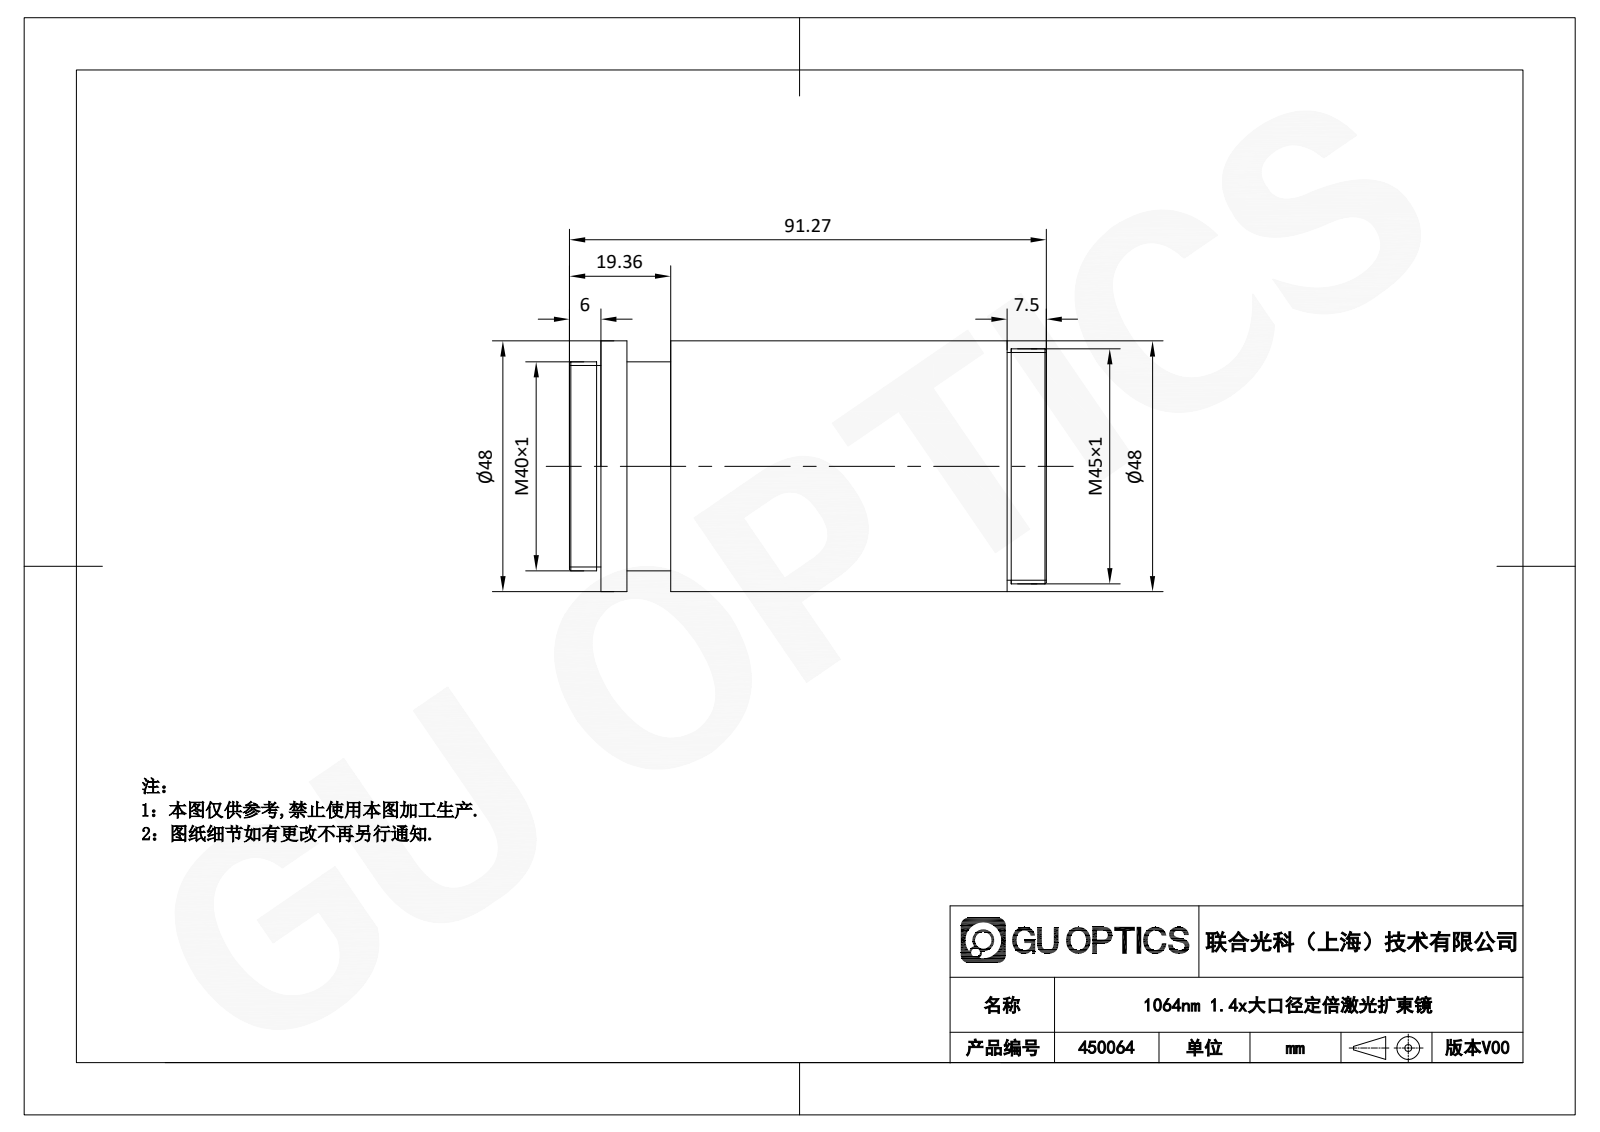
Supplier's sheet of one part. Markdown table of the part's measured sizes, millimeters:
| quantity | value |
| --- | --- |
| part name | 450064 |
| STEP written by | SolidWorks 2020 (AUTOMOTIVE_DESIGN) |
| units | millimeters |
| bodies | 1 solid, 26 faces (8 planar, 14 cylindrical, 4 other) |
| overall size | 91.27 × 48 × 48 |
| volume | 154 794 mm³ |
| surface area | 18 752 mm² |
| round bosses / shafts (diameter × count) | 48 × 1, 45 × 1, 42 × 1, 40 × 1, 37 × 1 |
| main face-to-face distances | 91.27, 6, 85.27, 19.36, 13.36, 71.91, 11, 5, 8.36, 80.27 |
